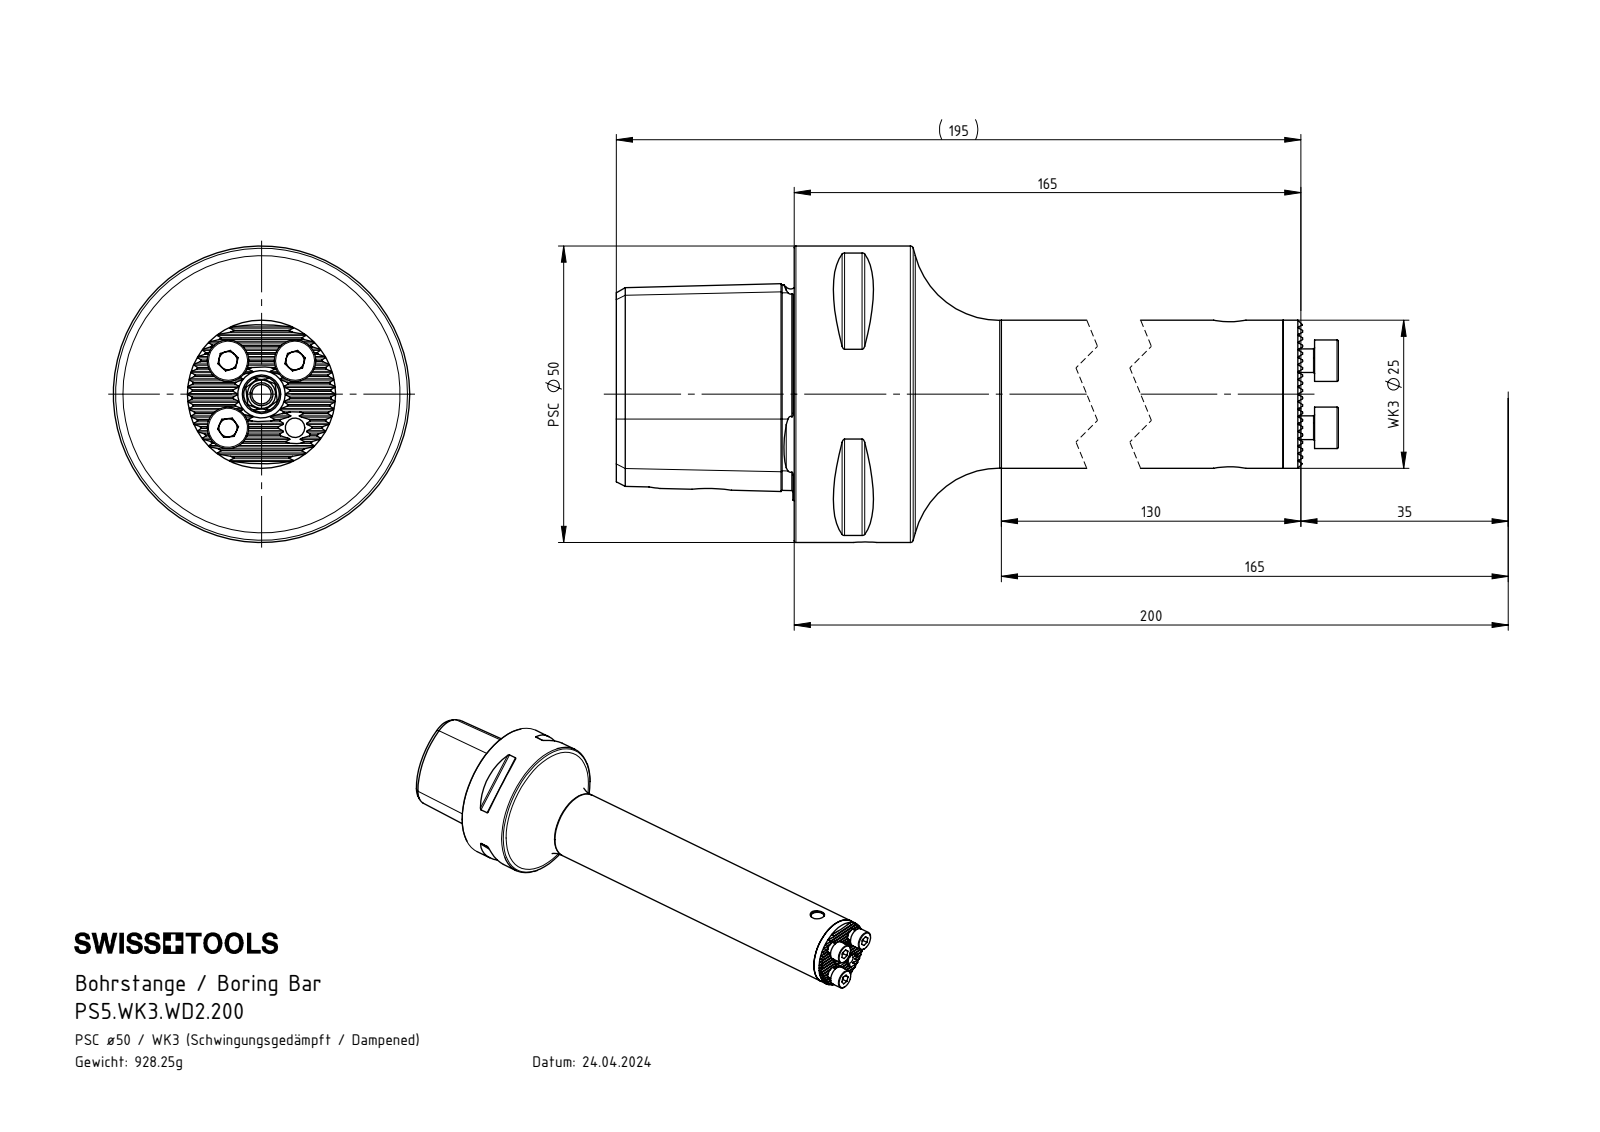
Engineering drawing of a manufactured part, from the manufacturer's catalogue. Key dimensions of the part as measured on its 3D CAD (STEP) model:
Part name (STEP PRODUCT): DIN 6325_ø5x10-m6_2x6; PS5-WD2.085.162_A_mit Stiftbohrung; DIN 3771 - 10x4; WD2-ER1.021.019_A (+8 more)
STEP written by: SolidWorks 2022 (AUTOMOTIVE_DESIGN)
Units: millimetres
Bodies: 16 solids, 682 faces (236 planar, 169 cylindrical, 277 other)
Overall size (bounding box): 201.3 × 50 × 50
Volume: 121 134 mm³ · Surface area: 51 336 mm²
Round holes (diameter × count): ⌀3.3 ×5, ⌀4 ×1, ⌀5 ×1, ⌀5.5 ×1, ⌀6 ×1, ⌀6.1 ×1, ⌀6.5 ×1, ⌀6.8 ×1, ⌀7.4 ×1, ⌀8.5 ×1, ⌀9 ×1, ⌀11 ×1
Round bosses / shafts (diameter × count): ⌀7 ×3, ⌀4 ×3, ⌀50 ×1, ⌀25 ×1, ⌀21 ×1, ⌀20.7 ×1, ⌀20 ×1, ⌀17.8 ×1
Partial cylindrical surfaces — rounded edges, fillets, slot ends (radius × count): R0.12 ×19, R0.5 ×8, R4 ×1
Main face-to-face distances: 6, 78.4, 30, 3.2, 4.33, 176, 146, 1.08, 9.2, 75.2
Hole centre spacings: 8, 11.32, 16.01, 26, 141, 167
